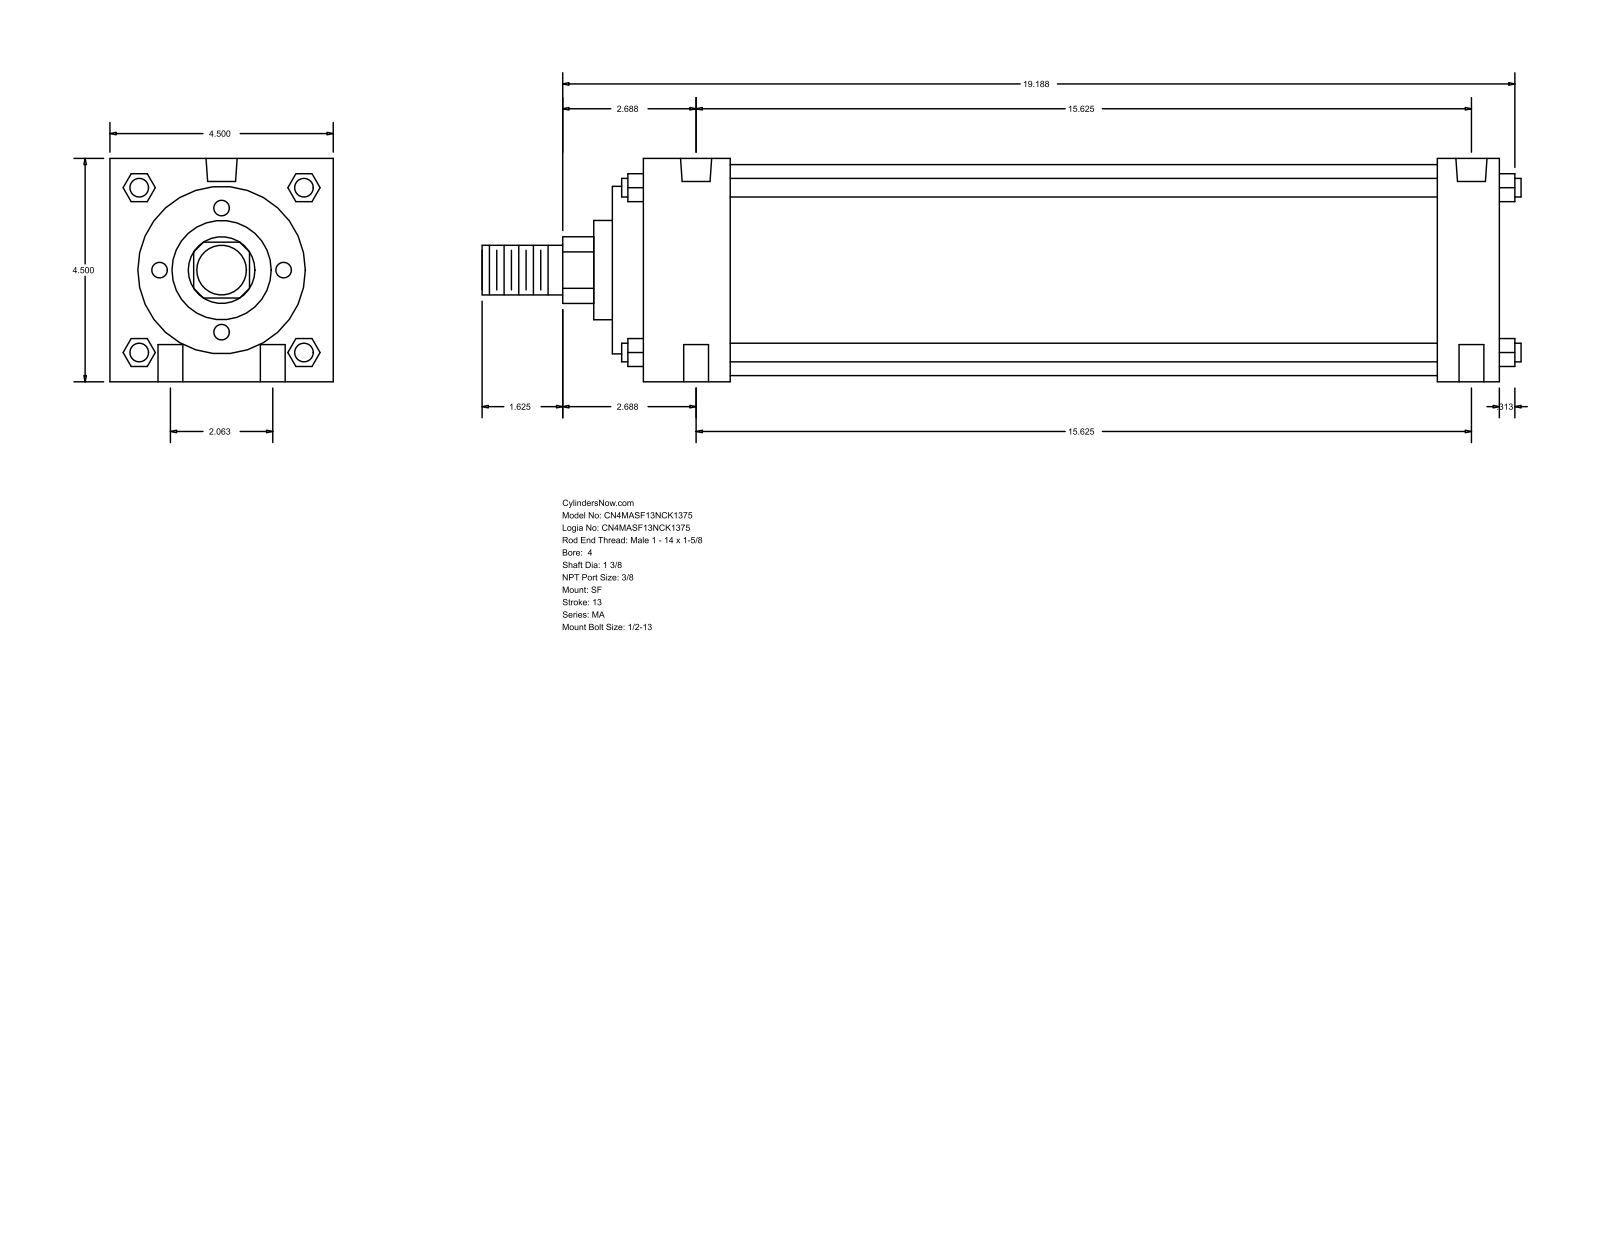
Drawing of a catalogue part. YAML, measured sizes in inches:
part_name: "MA_SF__0400_1.375"
step_written_by: "GSSL Pune (CONFIG_CONTROL_DESIGN)"
units: inches
bodies: {solids: 0, faces: 126, planar: 95, cylindrical: 31, other: 0}
overall_size: [20.937, 4.5, 4.5]
round_holes:
  - {diameter: 0.5, count: 4}
  - {diameter: 0.437, count: 2}
  - {diameter: 0.627, count: 2}
round_bosses_or_shafts:
  - {diameter: 0.375, count: 4}
  - {diameter: 4.25, count: 1}
  - {diameter: 3.375, count: 1}
  - {diameter: 2, count: 1}
  - {diameter: 1.375, count: 1}
  - {diameter: 1, count: 1}
partial_cylinders:
  - {radius: 0.672, count: 1}
face_to_face_distances: [4.5, 17.25, 0.625, 17.875, 16.625, 16, 1.25, 2.375, 1.75, 14.25]
hole_center_spacings: [1.031, 15.659, 15.625, 2.062, 15.761, 15.25]
